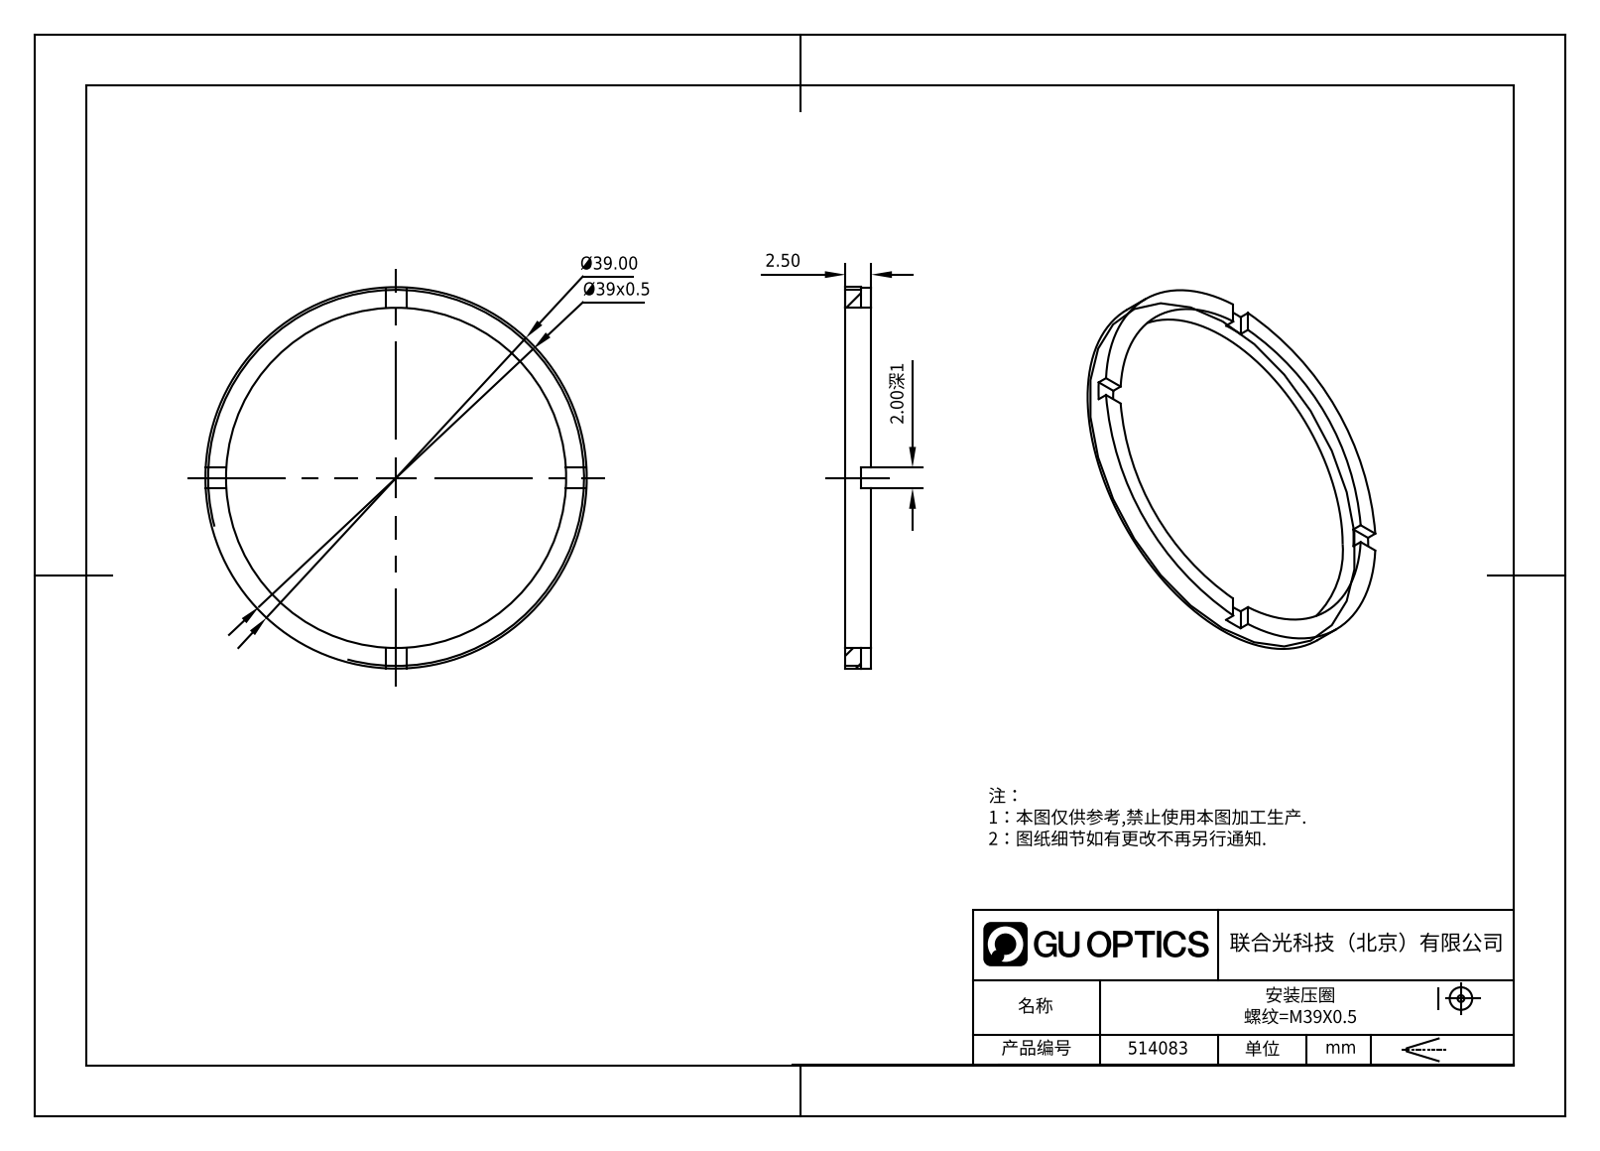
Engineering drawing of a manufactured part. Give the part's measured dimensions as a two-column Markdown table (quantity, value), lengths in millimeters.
| quantity | value |
| --- | --- |
| part name | 514083 |
| STEP written by | SolidWorks 2020 (CONFIG_CONTROL_DESIGN) |
| units | millimeters |
| bodies | 1 solid, 21 faces (17 planar, 4 cylindrical, 0 other) |
| overall size | 39 × 39 × 2.5 |
| volume | 565 mm³ |
| surface area | 1 046 mm² |
| round holes (diameter × count) | 35 × 1 |
| round bosses / shafts (diameter × count) | 39 × 1 |
| main face-to-face distances | 2.5, 1.5, 1, 2 |
